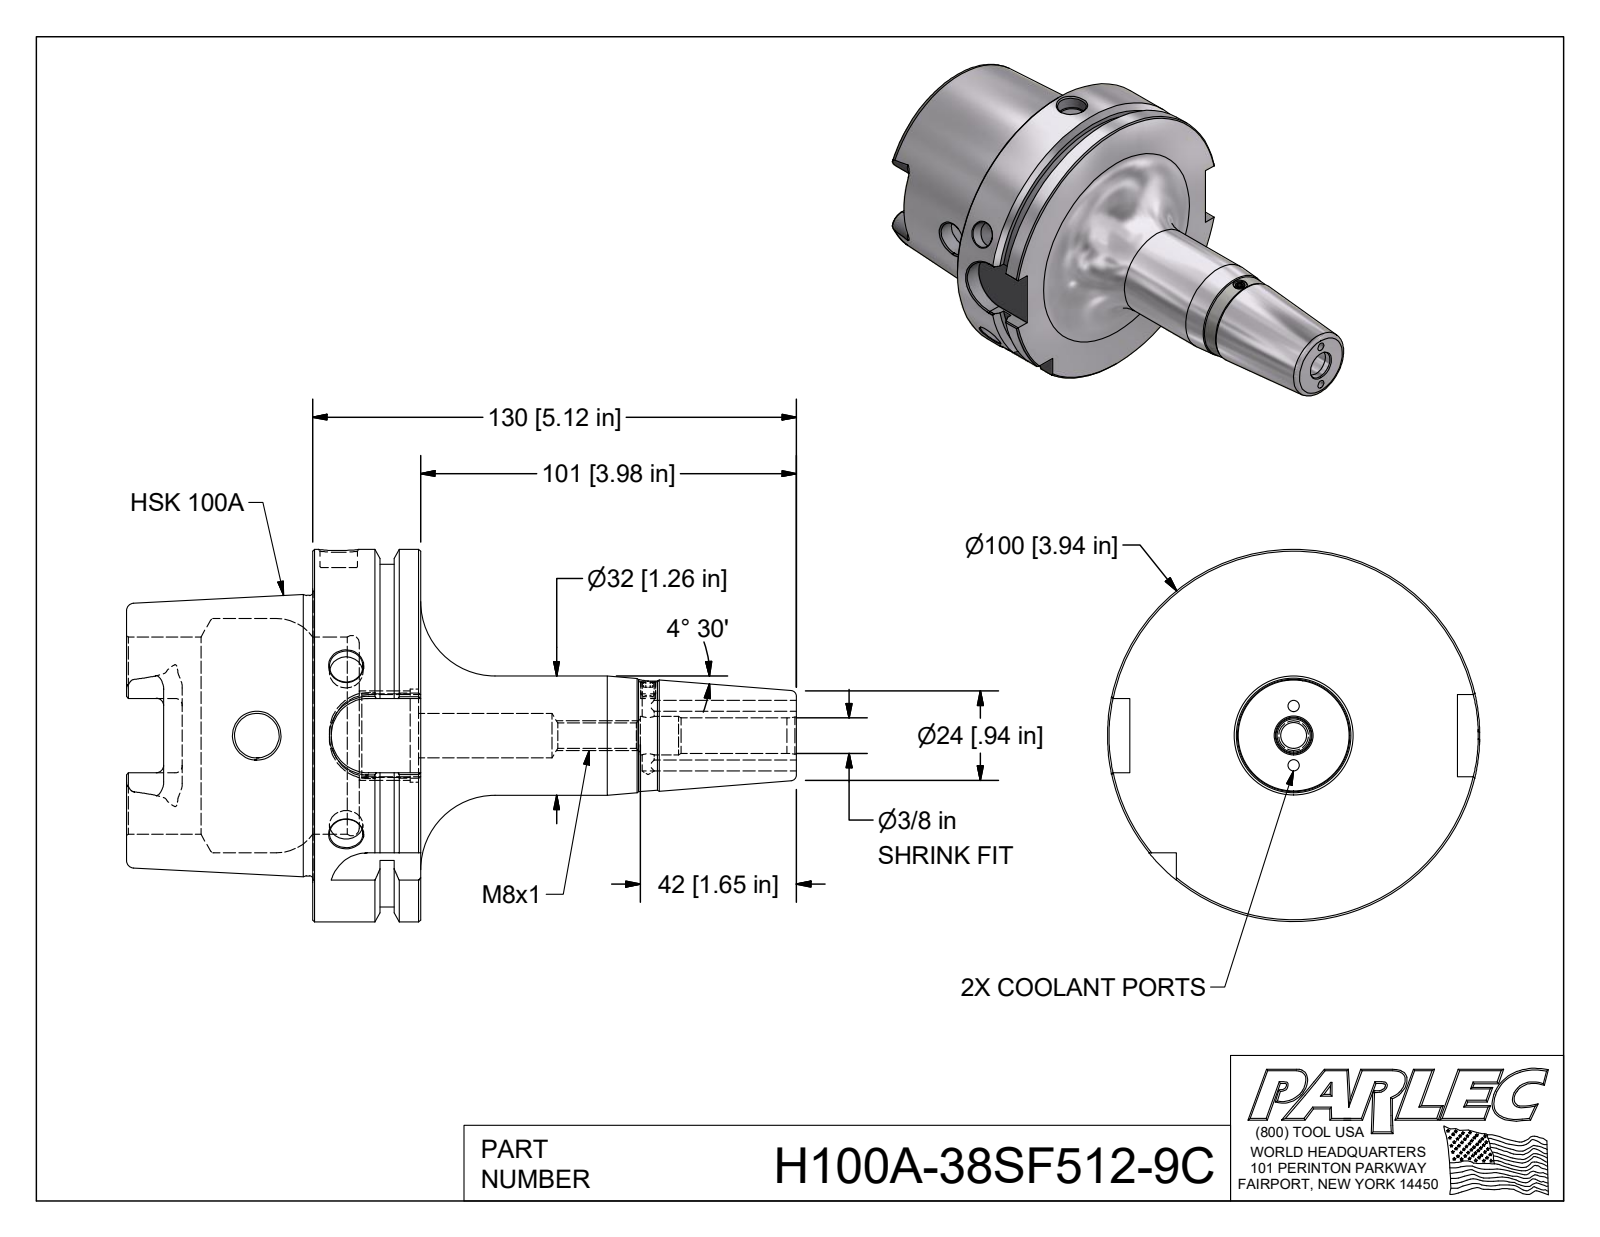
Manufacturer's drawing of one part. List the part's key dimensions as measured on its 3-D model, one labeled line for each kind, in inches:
STEP written by: Autodesk Inventor 2018 (AUTOMOTIVE_DESIGN)
Units: inches
Bodies: 1 solid, 154 faces (49 planar, 42 cylindrical, 63 other)
Overall size (bounding box): 7.087 × 3.937 × 3.937
Volume: 20.01 in³ · Surface area: 96.7 in²
Round holes (diameter × count): ⌀0.118 ×2, ⌀0.354 ×2, ⌀0.472 ×2, ⌀0.128 ×1, ⌀0.197 ×1, ⌀0.272 ×1, ⌀0.374 ×1, ⌀0.394 ×1, ⌀0.404 ×1, ⌀0.881 ×1, ⌀0.985 ×1, ⌀2.087 ×1
Round bosses / shafts (diameter × count): ⌀3.937 ×1, ⌀3.622 ×1, ⌀2.967 ×1, ⌀1.26 ×1
Partial cylindrical surfaces — rounded edges, fillets, slot ends (radius × count): R0.079 ×6, R0.192 ×4, R0.394 ×4
Main face-to-face distances: 1.142, 0.492, 0.65, 1.969, 2.461, 3.11, 3.465, 2.83, 0.861, 0.369
Hole centre spacings: 0.315, 0.63, 3.272
